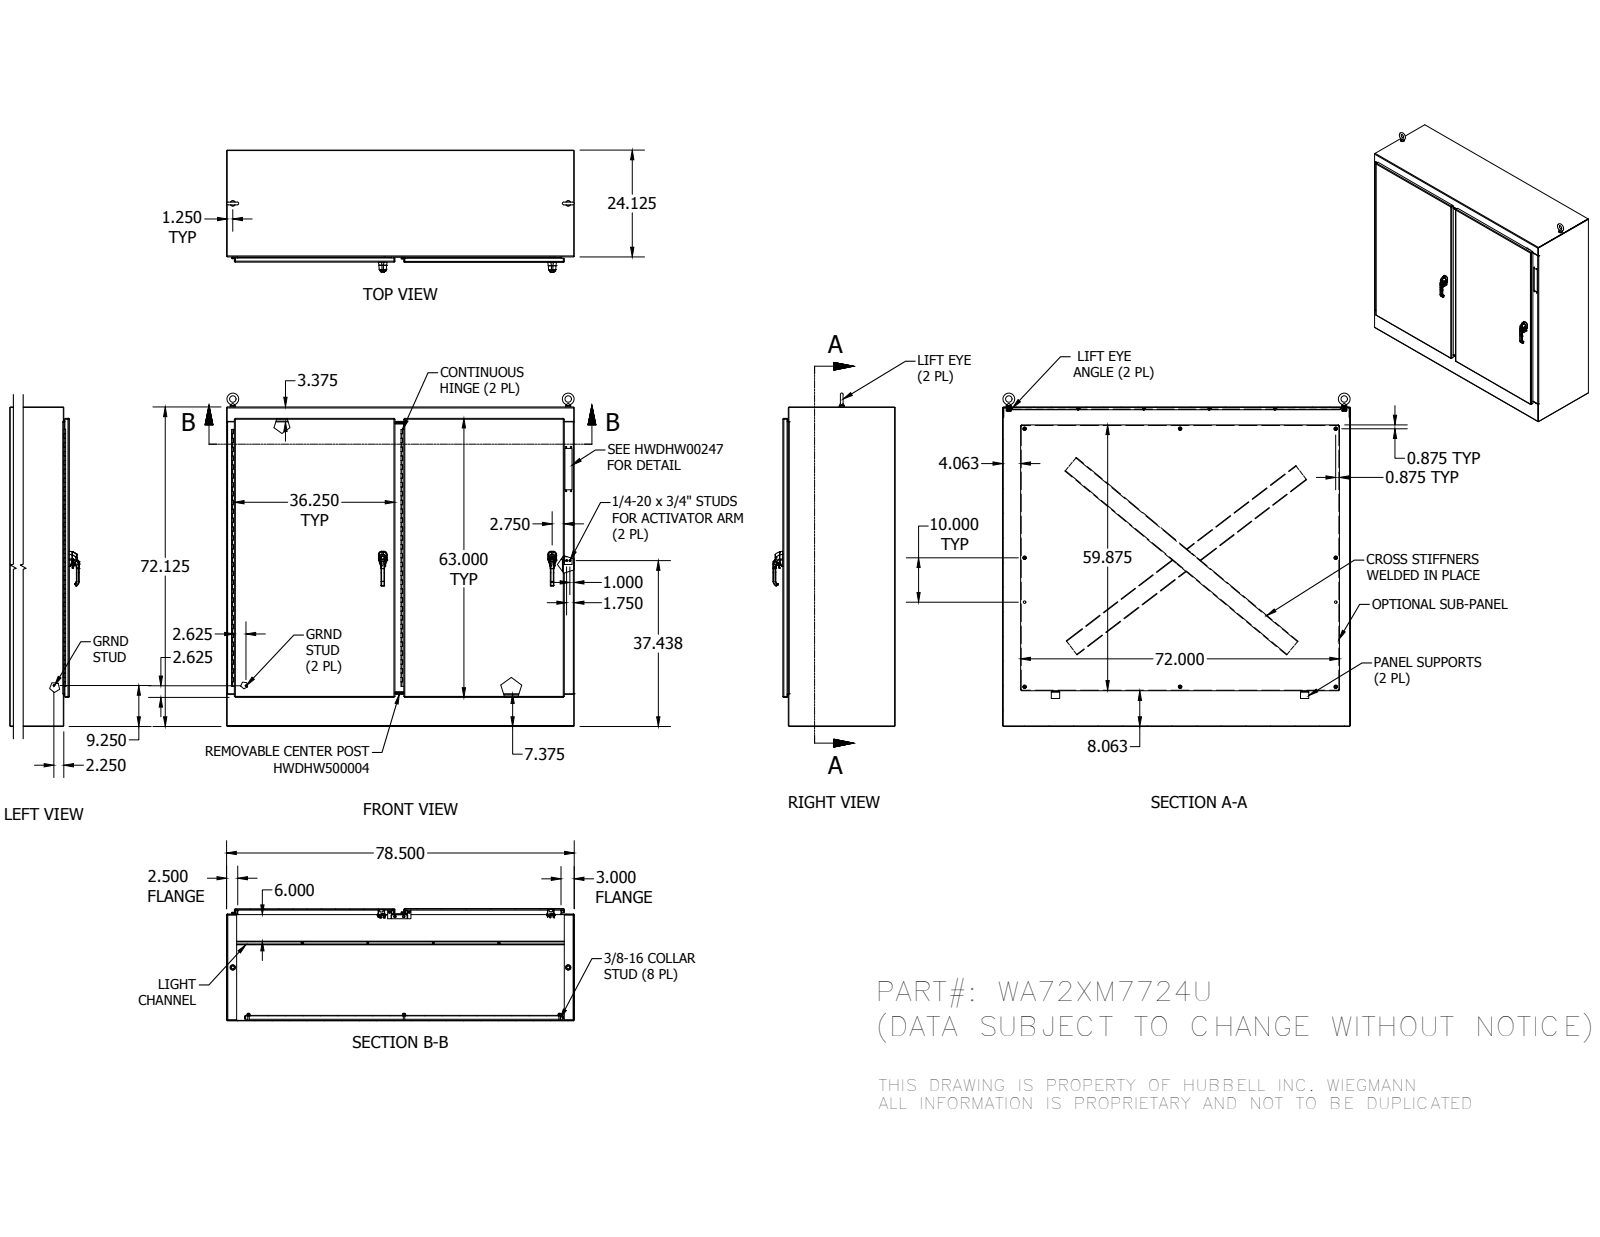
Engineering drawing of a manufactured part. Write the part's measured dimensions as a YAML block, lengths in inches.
part_name: "WA72XM77U_BACK; 3889; 349104; HFW3878 (+8 more)"
step_written_by: "Autodesk Inventor 2014 (AUTOMOTIVE_DESIGN)"
units: inches
bodies: {solids: 226, faces: 8866, planar: 4140, cylindrical: 2898, other: 1828}
overall_size: [78.5, 75.248, 27.604]
volume: 2660
surface_area: 43590
round_holes:
  - {diameter: 0.25, count: 18}
  - {diameter: 0.375, count: 18}
  - {diameter: 0.276, count: 16}
  - {diameter: 0.281, count: 10}
  - {diameter: 0.19, count: 8}
  - {diameter: 0.2, count: 8}
  - {diameter: 0.289, count: 8}
  - {diameter: 0.307, count: 8}
  - {diameter: 0.313, count: 8}
  - {diameter: 0.335, count: 8}
  - {diameter: 0.38, count: 8}
  - {diameter: 0.196, count: 7}
round_bosses_or_shafts:
  - {diameter: 0.33, count: 18}
  - {diameter: 0.25, count: 18}
  - {diameter: 0.625, count: 13}
  - {diameter: 0.375, count: 12}
  - {diameter: 0.337, count: 12}
  - {diameter: 0.563, count: 9}
  - {diameter: 0.28, count: 8}
  - {diameter: 1, count: 7}
partial_cylinders:
  - {radius: 0.02, count: 357}
  - {radius: 0.012, count: 215}
  - {radius: 0.02, count: 192}
  - {radius: 0.019, count: 42}
  - {radius: 0.05, count: 32}
  - {radius: 0.079, count: 28}
  - {radius: 0.063, count: 24}
  - {radius: 0.059, count: 23}
face_to_face_distances: [0.125, 0.125, 0.063, 0.188, 25.23, 25.105, 25.167, 25.042, 25.292, 25.355]
hole_center_spacings: [53.987, 54.737, 0.063, 54.363, 54.738, 55.112, 0.38, 1.601]
